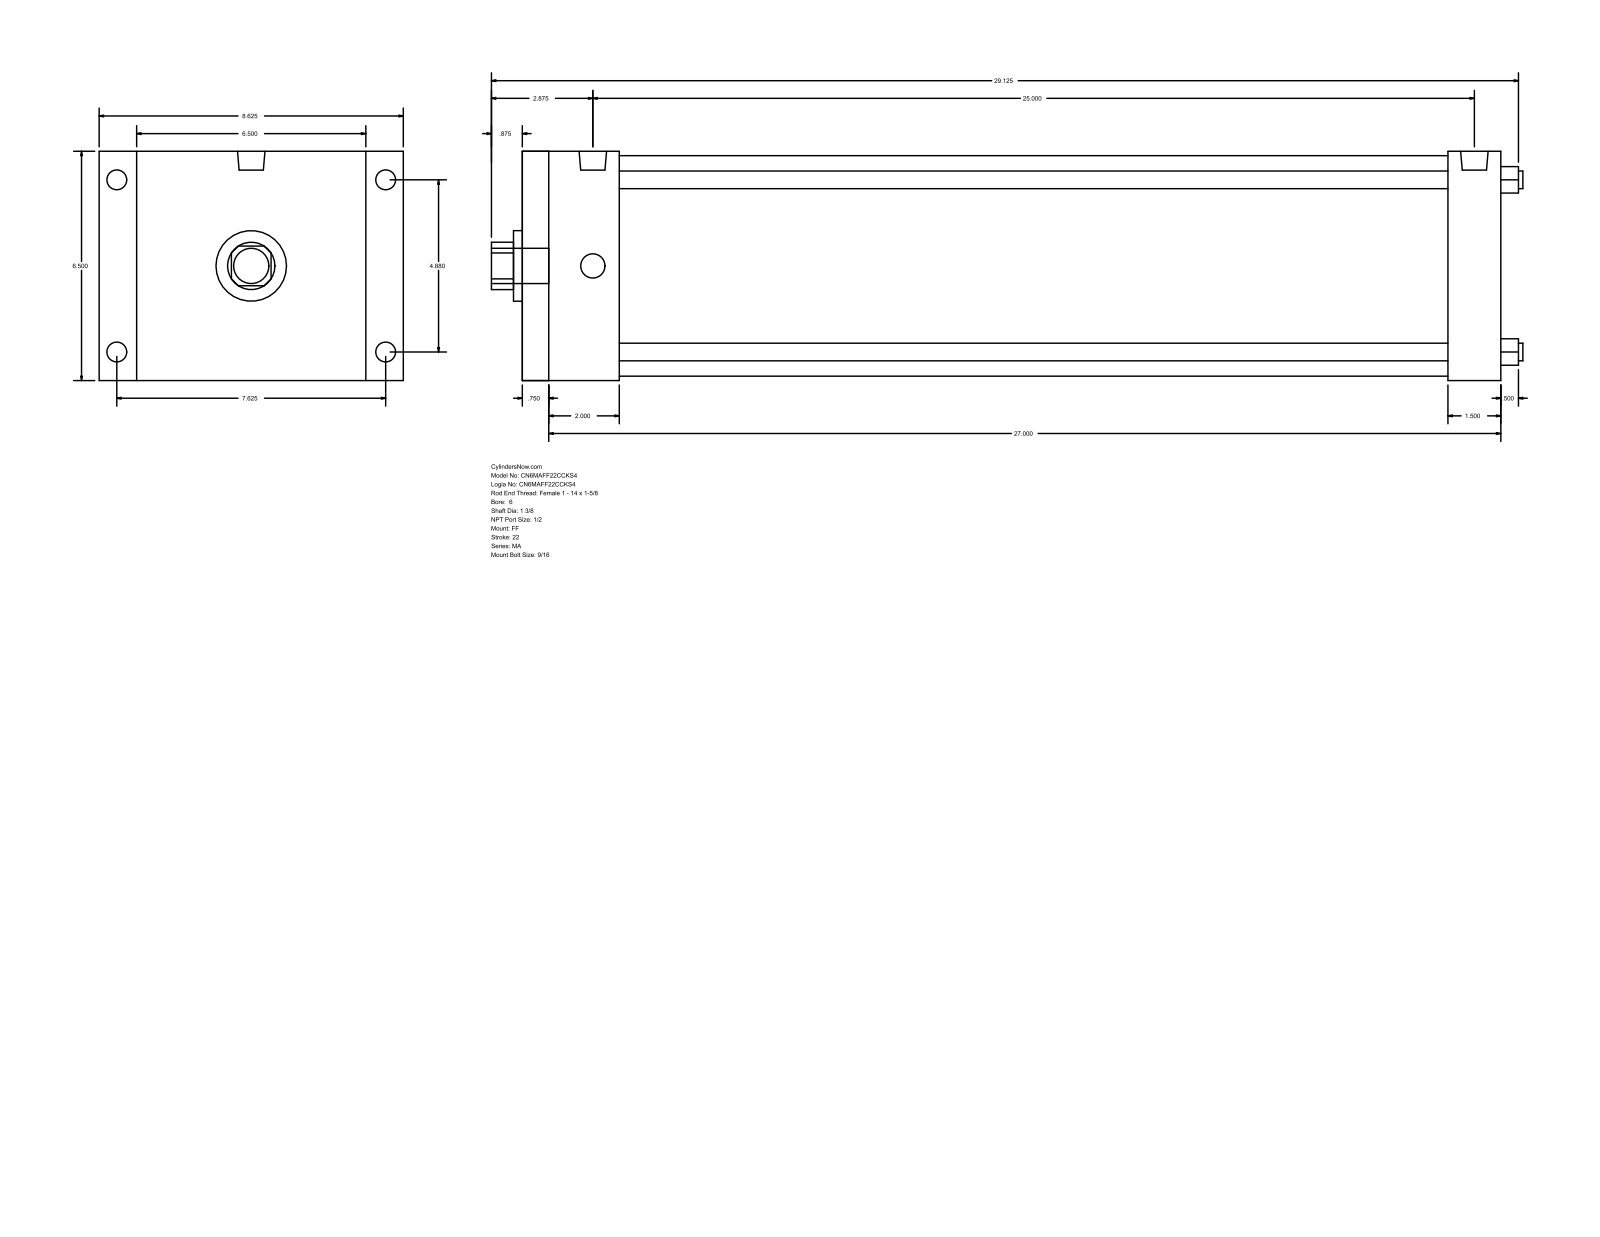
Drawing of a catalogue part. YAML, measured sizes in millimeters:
part_name: "MA_FF__0600_1.375"
step_written_by: "GSSL Pune (CONFIG_CONTROL_DESIGN)"
units: millimeters
bodies: {solids: 0, faces: 92, planar: 64, cylindrical: 28, other: 0}
overall_size: [742.95, 219.07, 165.1]
round_holes:
  - {diameter: 12.7, count: 4}
  - {diameter: 34.92, count: 1}
  - {diameter: 50.8, count: 1}
  - {diameter: 158.75, count: 1}
round_bosses_or_shafts:
  - {diameter: 17.46, count: 4}
  - {diameter: 14.29, count: 4}
  - {diameter: 19.77, count: 2}
  - {diameter: 25.4, count: 1}
partial_cylinders:
  - {radius: 17.06, count: 1}
face_to_face_distances: [165.1, 704.85, 15.87, 688.98, 38.1, 66.67, 50.8, 638.18, 666.75, 650.88]
hole_center_spacings: [87.65, 123.96, 175.31]
